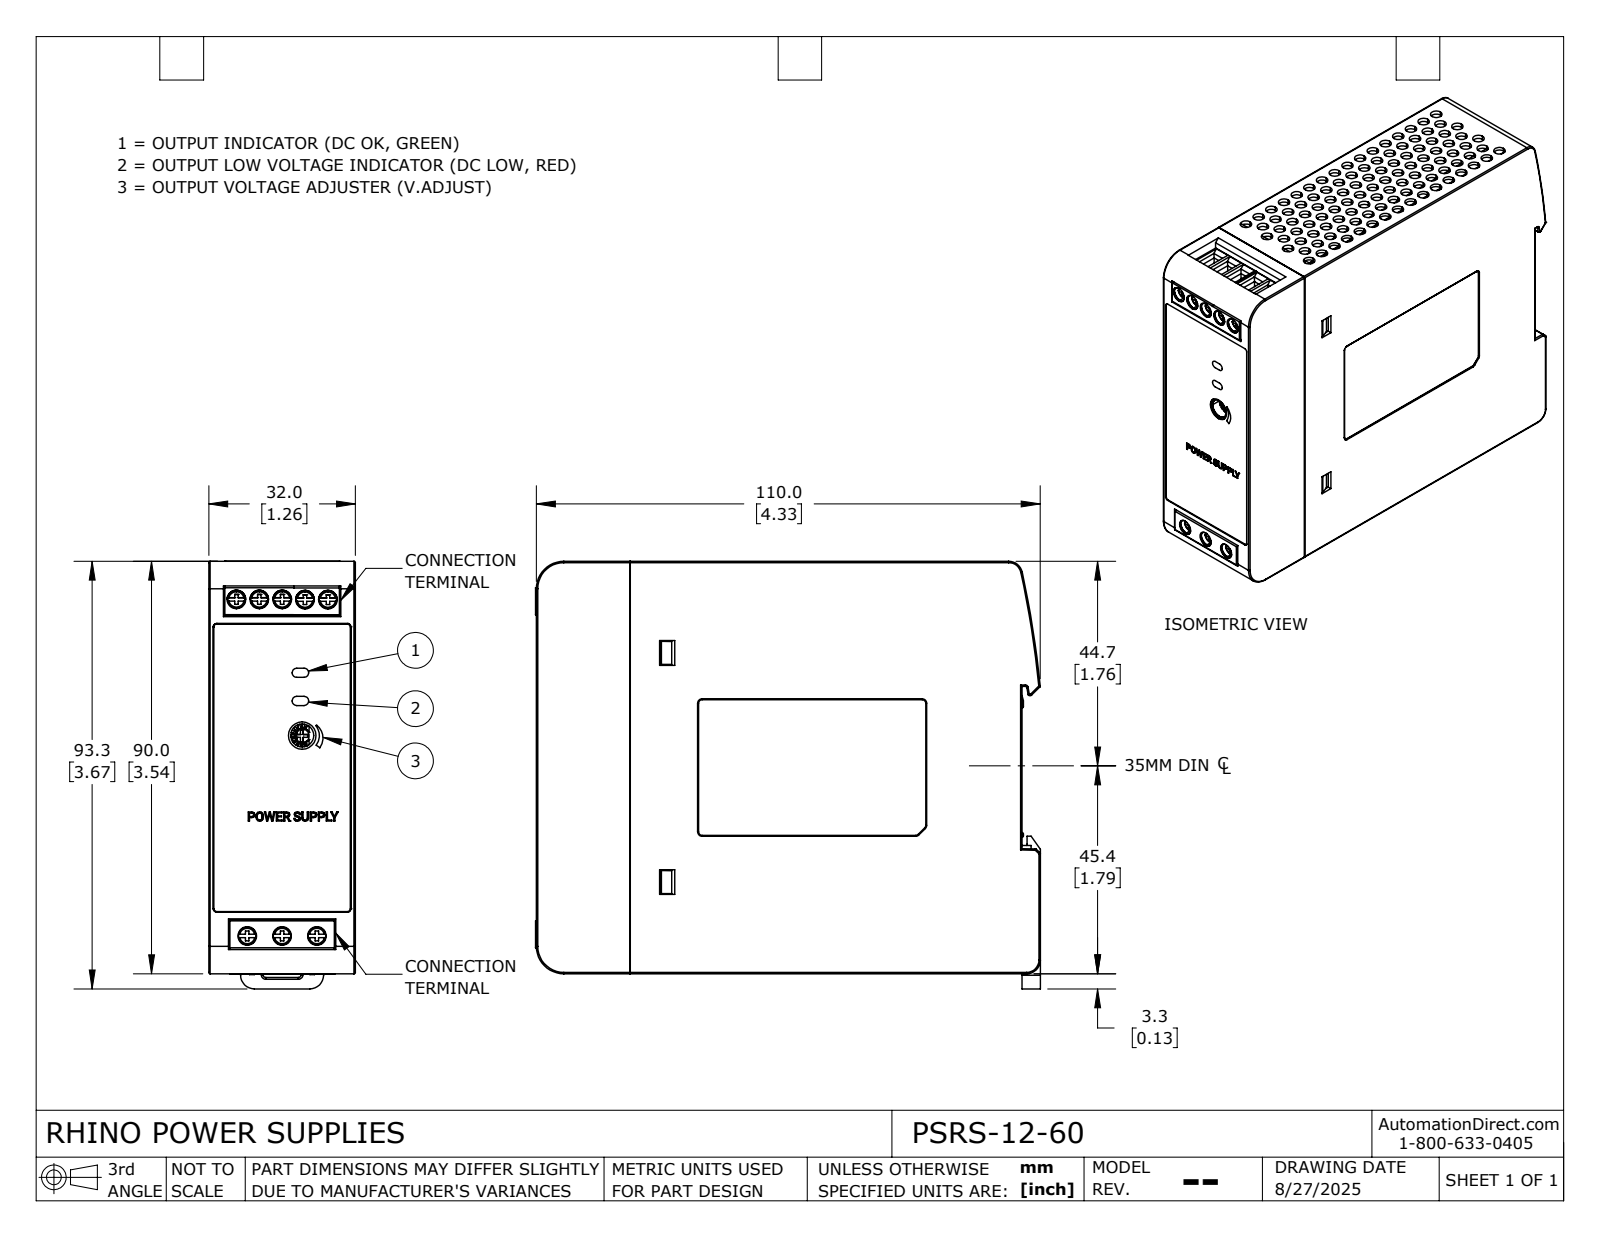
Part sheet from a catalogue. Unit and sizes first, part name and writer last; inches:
Units: inches
Overall size (bounding box): 4.339 × 3.673 × 1.26
Round holes (diameter × count): ⌀0.15 ×8, ⌀0.159 ×8, ⌀0.134 ×1, ⌀0.197 ×1
Round bosses / shafts (diameter × count): ⌀0.156 ×8, ⌀0.118 ×1
Partial cylindrical surfaces — rounded edges, fillets, slot ends (radius × count): R0.012 ×49, R0.039 ×12, R0.004 ×10, R0.02 ×7, R0.118 ×4, R0.098 ×3, R0.008 ×2, R0.024 ×2
Main face-to-face distances: 1.26, 3.543, 1.254, 0.039, 4.167, 3.504, 0.157, 4.325, 3.465, 0.079
Hole centre spacings: 0.197, 0.299, 0.393, 0.589, 1.727, 2.891, 0.196, 0.394
Volume: 18.61 in³ · Surface area: 60.8 in²
Bodies: 1 solid, 1728 faces (941 planar, 192 cylindrical, 595 other)
Part name (STEP PRODUCT): SPB-A060-12
STEP written by: SolidWorks 2024 (AUTOMOTIVE_DESIGN)
